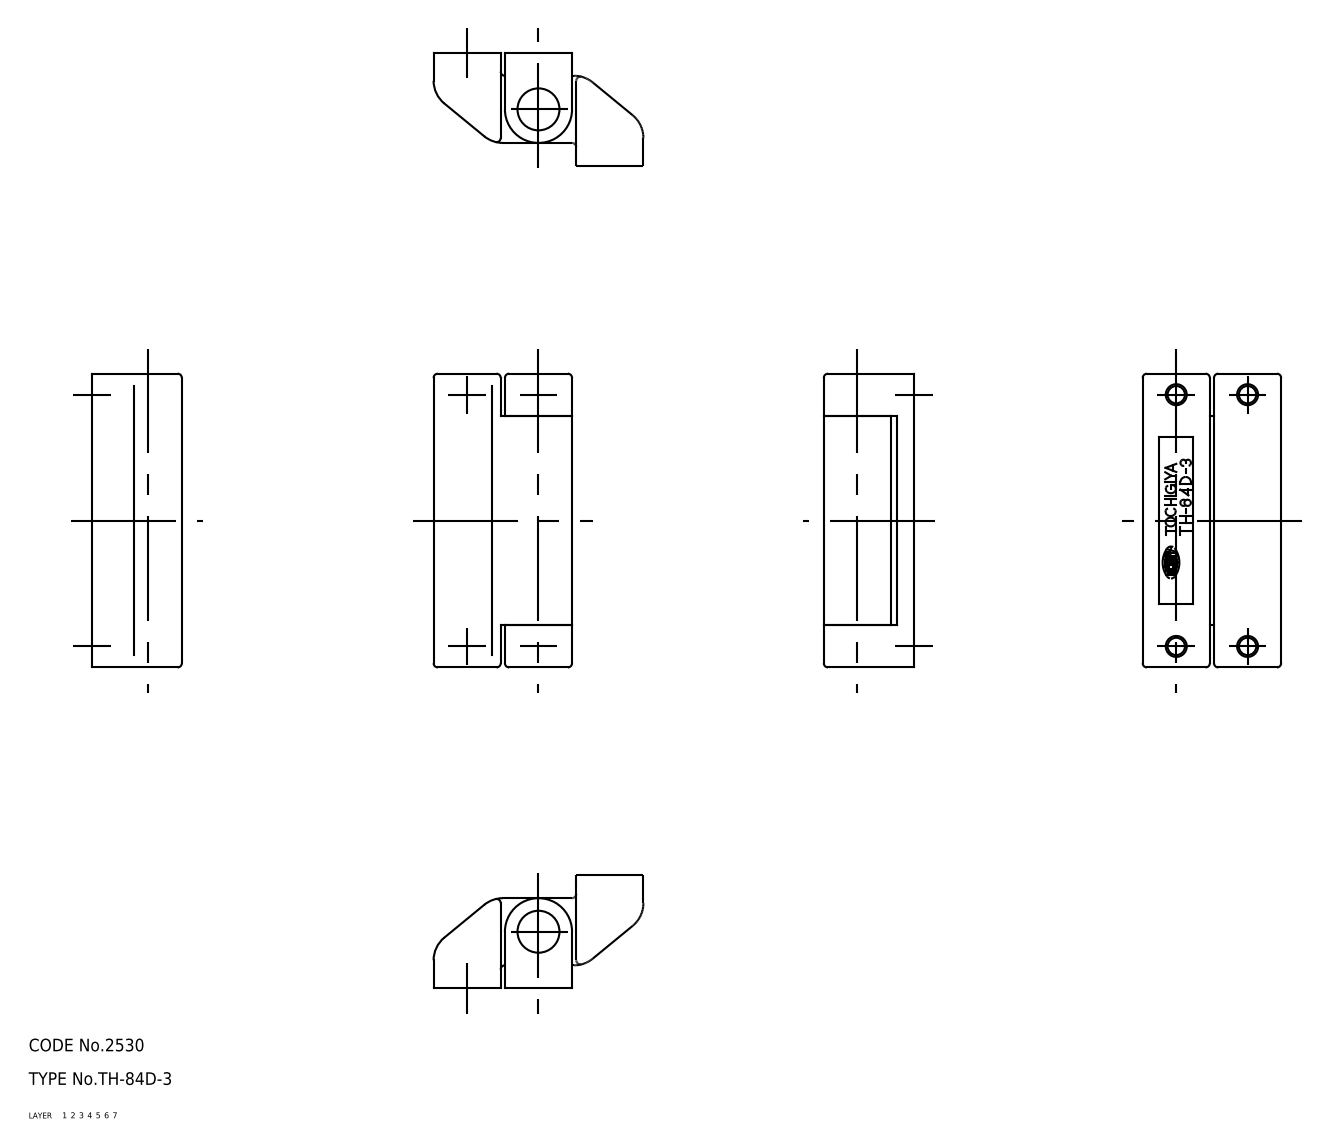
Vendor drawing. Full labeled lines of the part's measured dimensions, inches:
Part name (STEP PRODUCT): shaft; hinge piece_B; hinge piece_A; TH_84D_3_18147_36
STEP written by: CADfix (AUTOMOTIVE_DESIGN)
Units: inches
Bodies: 3 solids, 74 faces (0 planar, 0 cylindrical, 74 other)
Overall size (bounding box): 2.756 × 1.299 × 0.846
Volume: 2.398 in³ · Surface area: 24.74 in²
